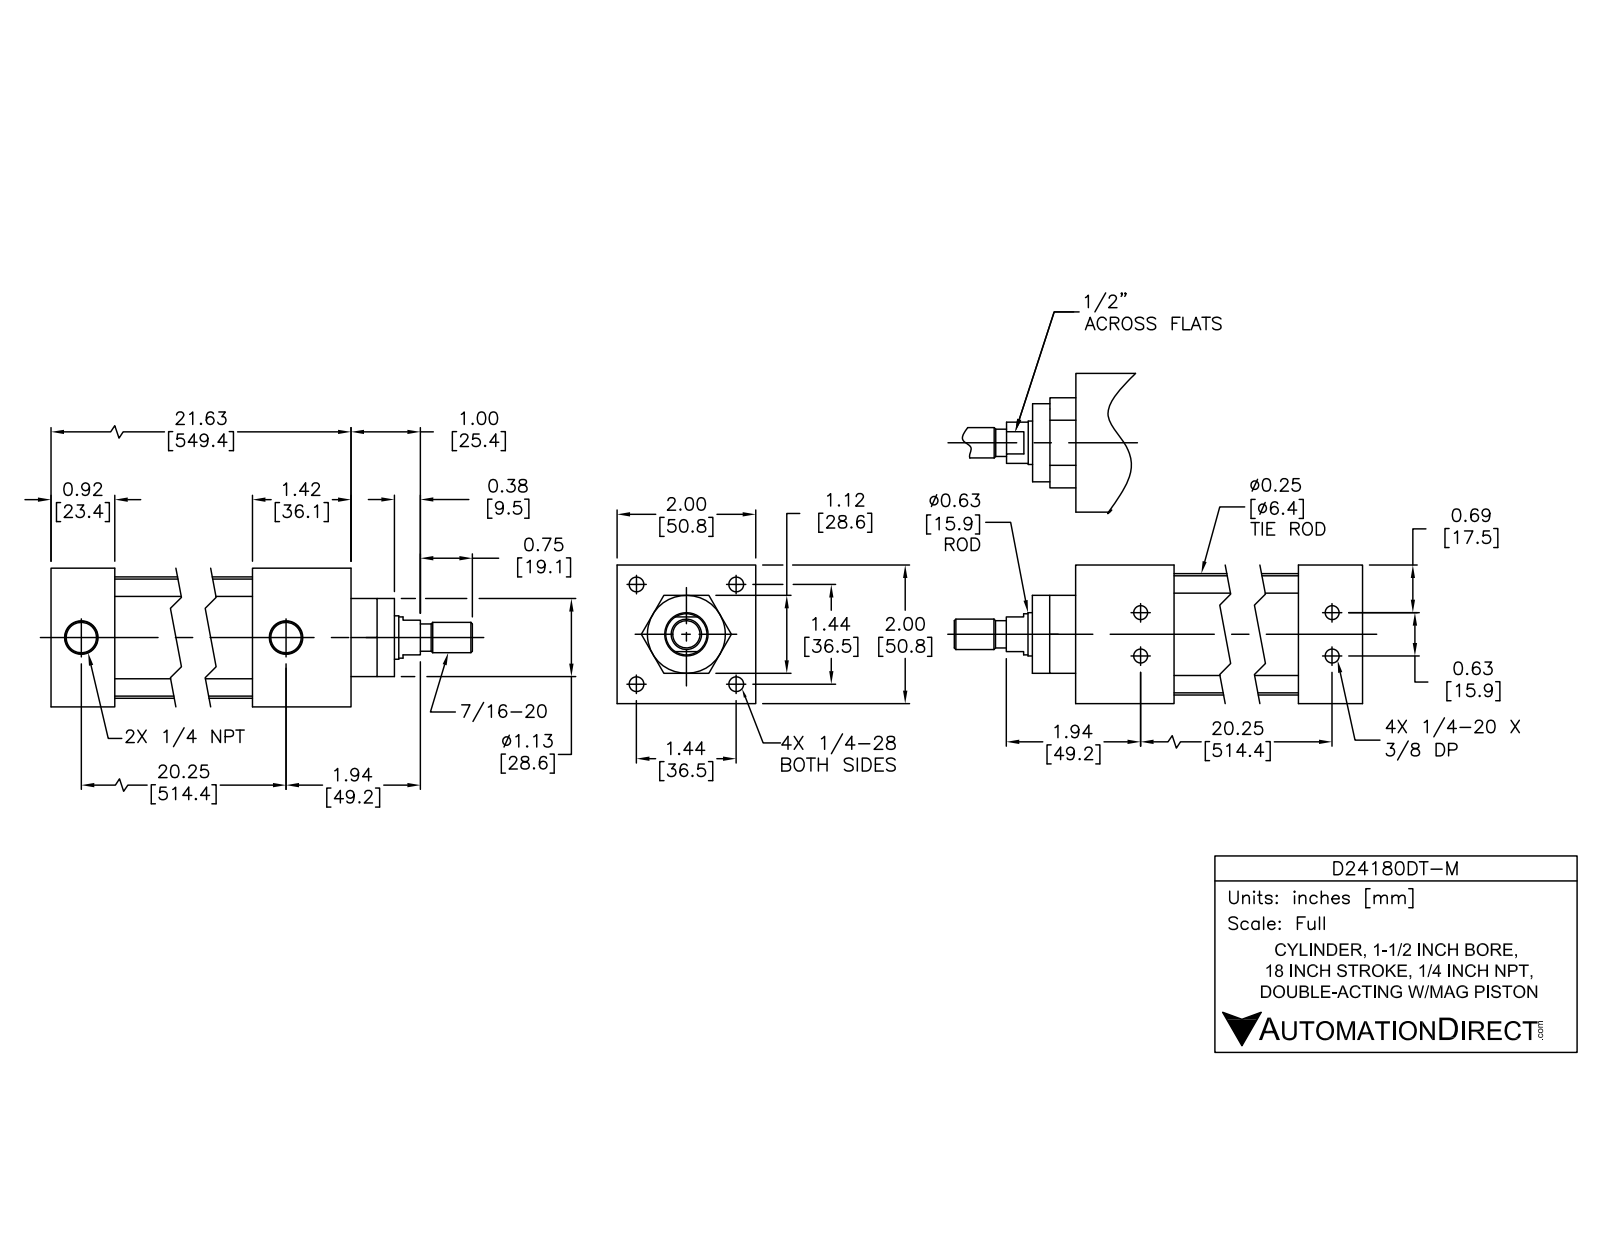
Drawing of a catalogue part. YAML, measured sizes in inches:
part_name: "D24180DT-M; D24180DT-M BODY; D24180DT-M PISTON"
step_written_by: "SolidWorks 2015 (AUTOMOTIVE_DESIGN)"
units: inches
bodies: {solids: 12, faces: 303, planar: 99, cylindrical: 114, other: 90}
overall_size: [23.371, 2, 2]
volume: 32.43
surface_area: 362.2
round_holes:
  - {diameter: 0.196, count: 4}
  - {diameter: 0.211, count: 4}
  - {diameter: 0.281, count: 4}
  - {diameter: 0.406, count: 4}
  - {diameter: 0.297, count: 2}
  - {diameter: 0.477, count: 2}
  - {diameter: 0.625, count: 1}
  - {diameter: 0.628, count: 1}
  - {diameter: 1.5, count: 1}
round_bosses_or_shafts:
  - {diameter: 0.39, count: 4}
  - {diameter: 0.25, count: 4}
  - {diameter: 0.222, count: 4}
  - {diameter: 1.75, count: 1}
  - {diameter: 1.497, count: 1}
  - {diameter: 1.121, count: 1}
  - {diameter: 0.622, count: 1}
  - {diameter: 0.59, count: 1}
partial_cylinders:
  - {radius: 0.2, count: 4}
face_to_face_distances: [2, 0.08, 19.201, 21.621, 1.42, 20.201, 20.701, 19.281, 0.92, 1.121]
hole_center_spacings: [1.014, 1.434, 20.248, 0.312, 0.313, 0.625, 2.028, 20.247]
